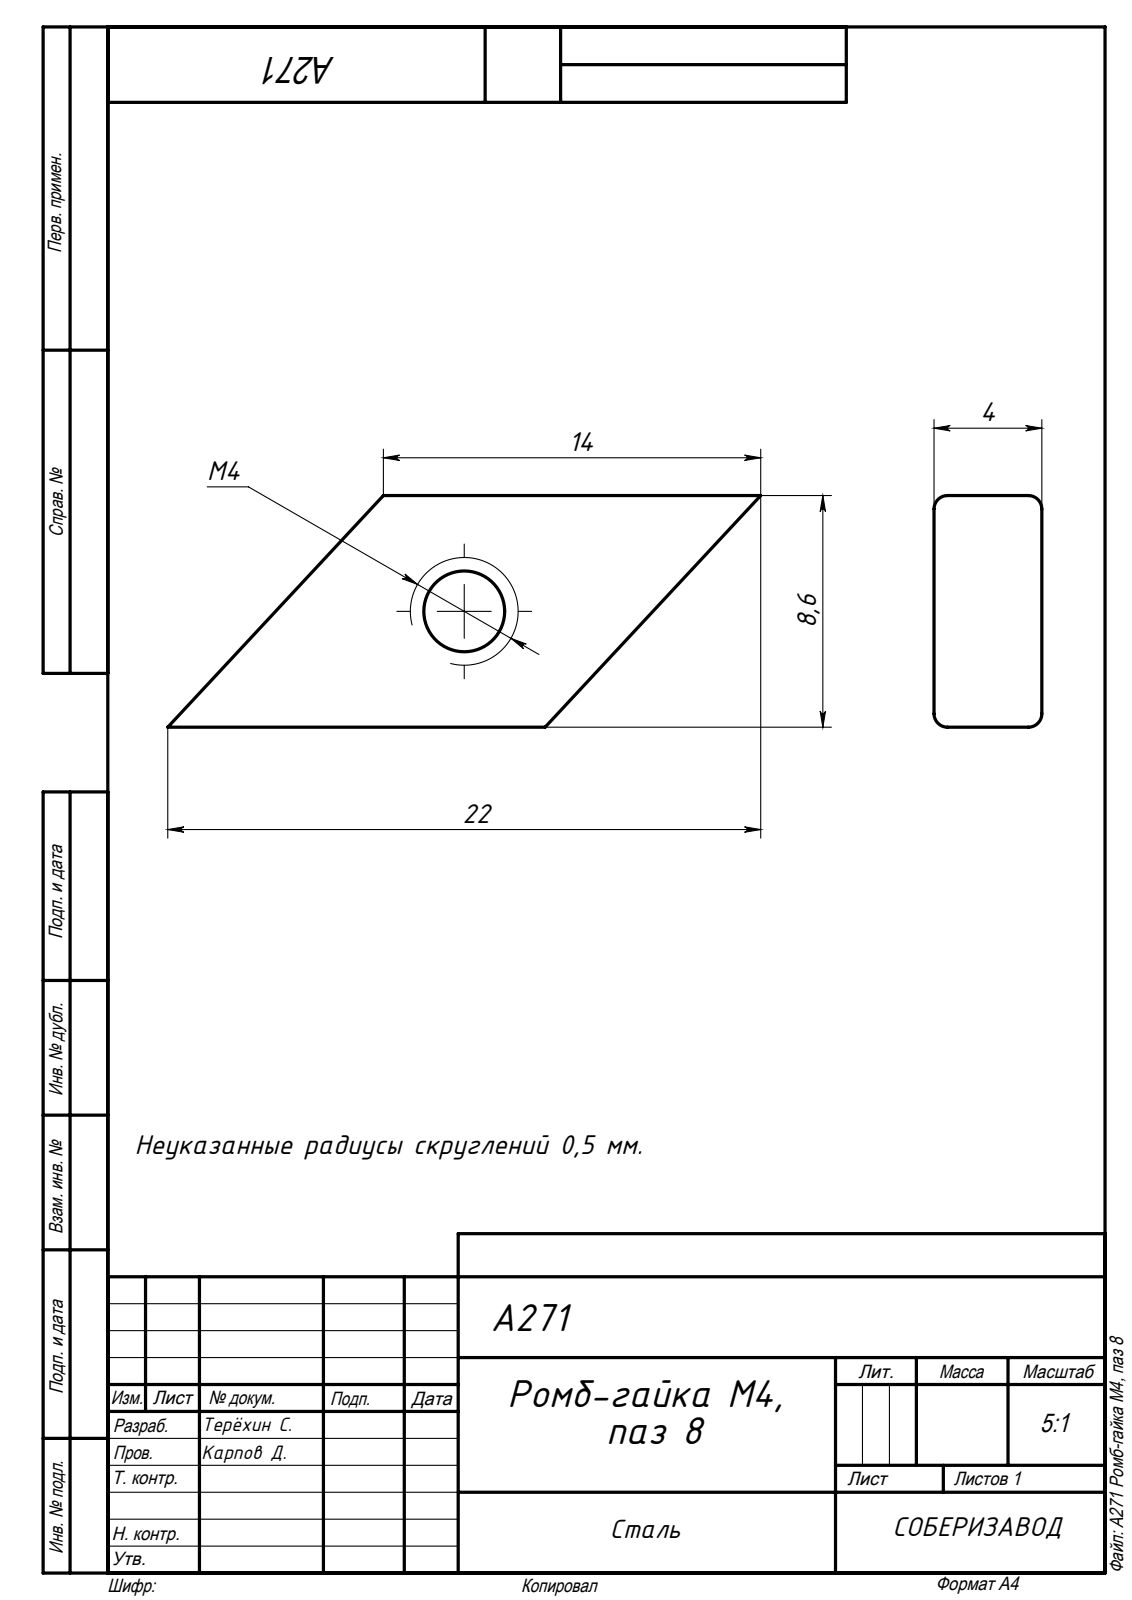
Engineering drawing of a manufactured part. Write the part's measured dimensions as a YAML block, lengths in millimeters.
part_name: "A271 Ромб-гайка М4, паз 8"
step_written_by: "SolidWorks 2020 (AUTOMOTIVE_DESIGN)"
units: millimeters
bodies: {solids: 1, faces: 16, planar: 6, cylindrical: 10, other: 0}
overall_size: [22, 8.6, 4]
volume: 448
surface_area: 448
round_holes:
  - {diameter: 3, count: 1}
partial_cylinders:
  - {radius: 0.5, count: 8}
face_to_face_distances: [4, 8.6, 10.24]
